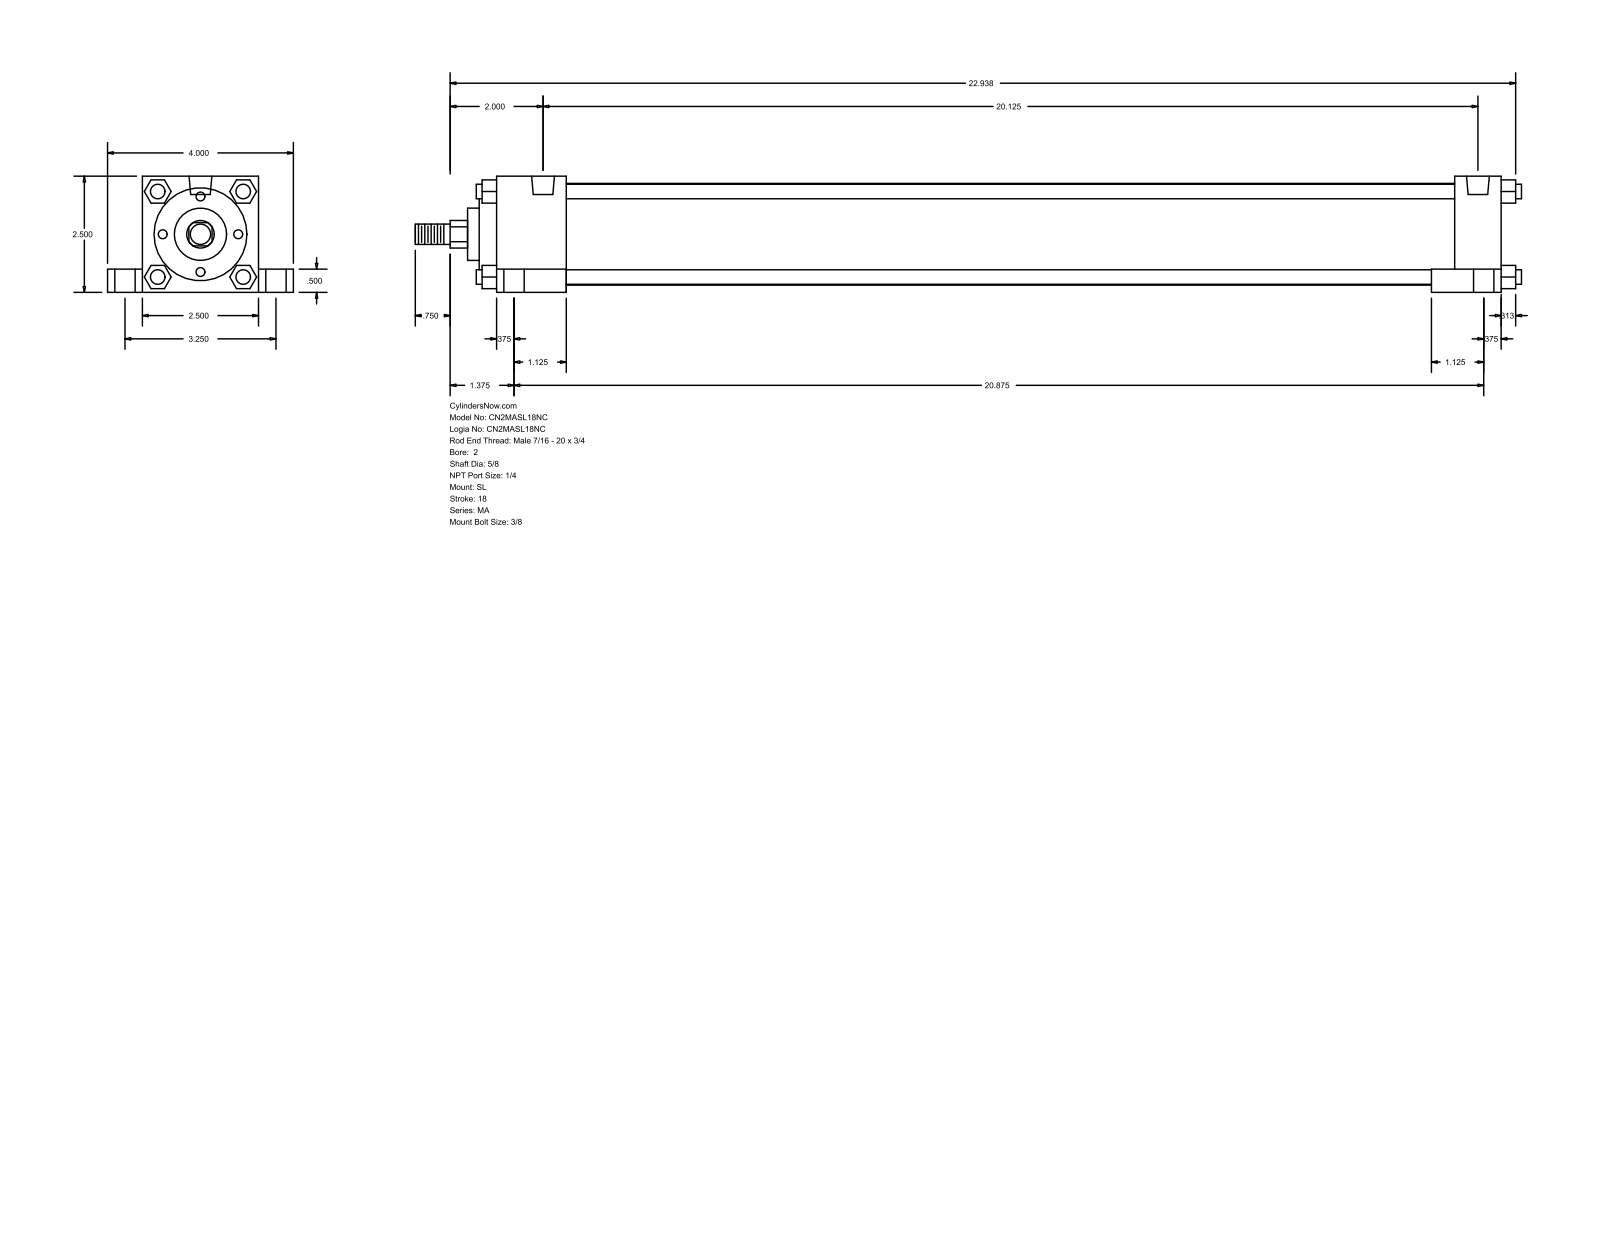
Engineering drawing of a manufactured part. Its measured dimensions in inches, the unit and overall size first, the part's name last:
Units: inches
Overall size (bounding box): 23.813 × 4 × 2.5
Round holes (diameter × count): ⌀0.313 ×4, ⌀0.437 ×4, ⌀0.687 ×4, ⌀0.492 ×2
Round bosses / shafts (diameter × count): ⌀0.313 ×4, ⌀2.19 ×1, ⌀2 ×1, ⌀1.125 ×1, ⌀0.625 ×1, ⌀0.437 ×1
Partial cylindrical surfaces — rounded edges, fillets, slot ends (radius × count): R0.297 ×1
Main face-to-face distances: 2.5, 0.5, 0.375, 19.125, 1, 0.75, 3.25, 1.5, 21.625, 2
Hole centre spacings: 1.63, 1.741, 3.25, 20.125, 20.315, 20.814, 20.875, 21.127
Bodies: 0 solids, 150 faces (113 planar, 37 cylindrical, 0 other)
Part name (STEP PRODUCT): MA_SL__0200_0.625
STEP written by: GSSL Pune (CONFIG_CONTROL_DESIGN)
